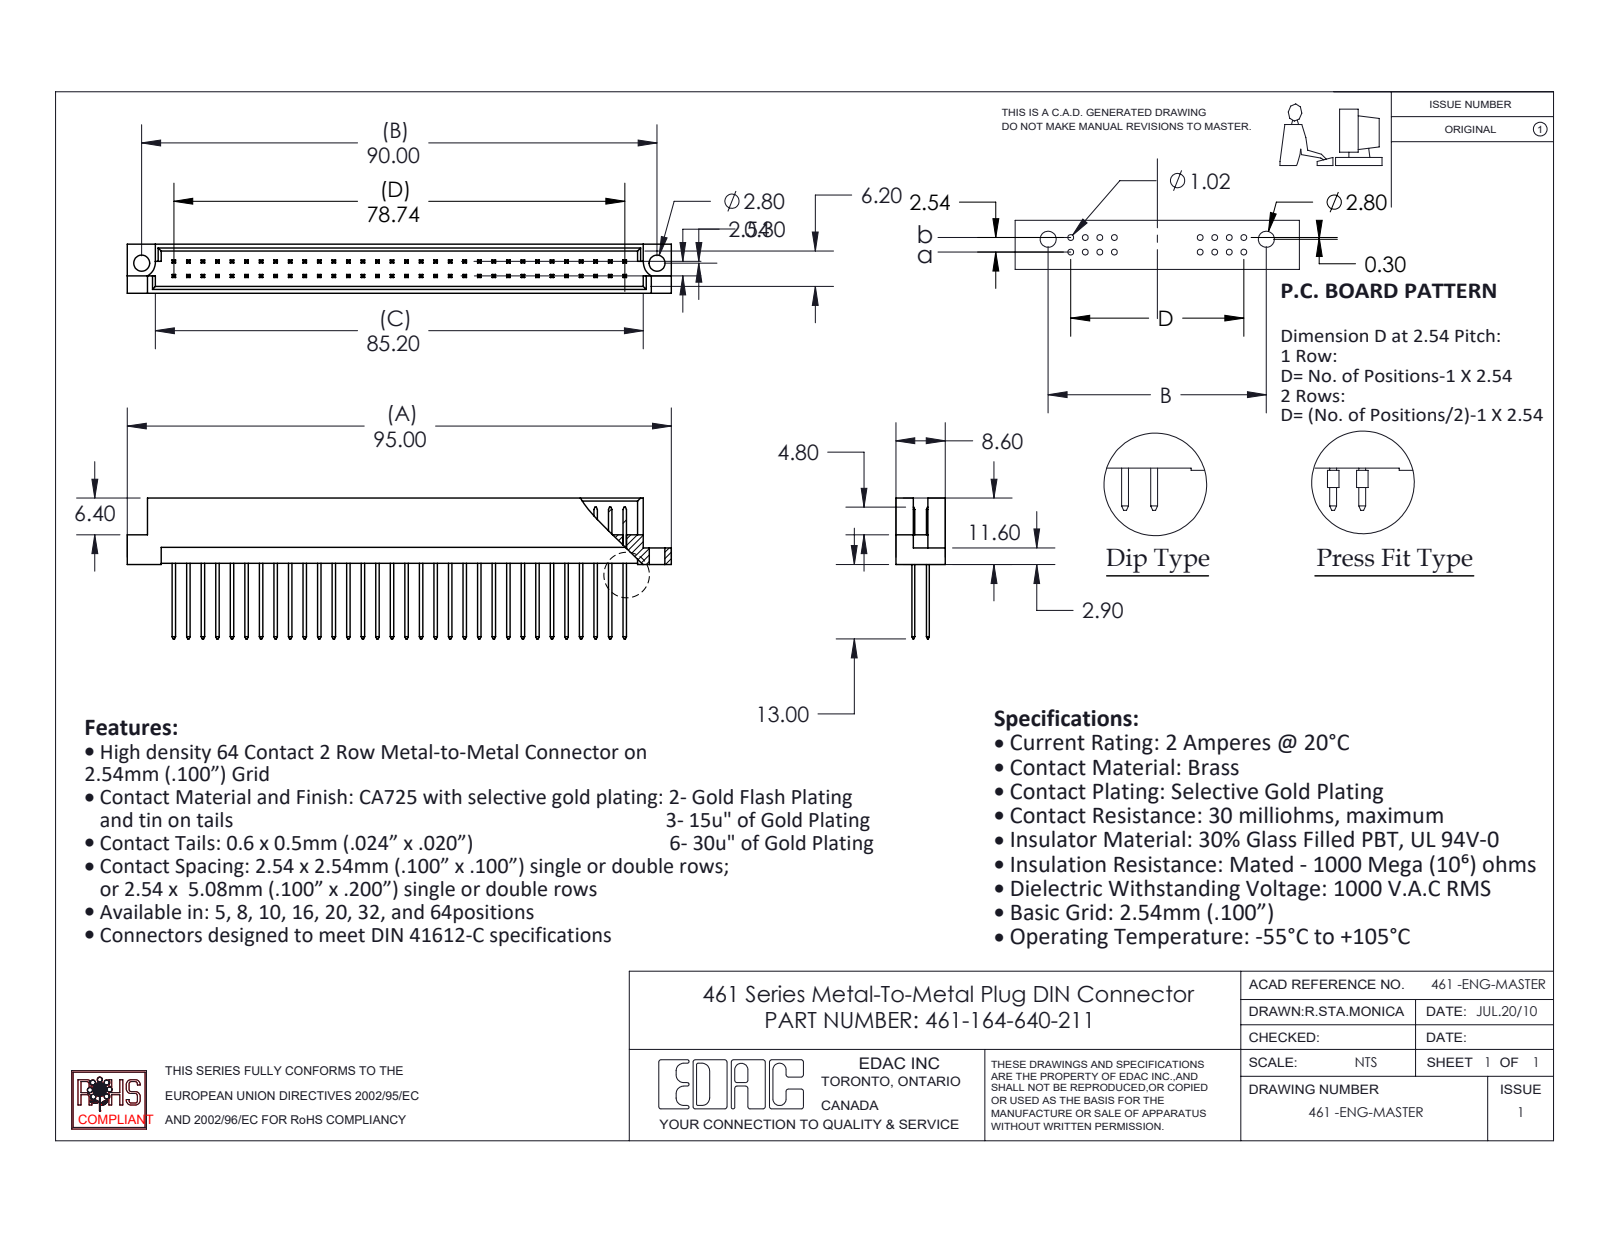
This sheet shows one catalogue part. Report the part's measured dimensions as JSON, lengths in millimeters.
{"part_name": "461 Part_64; 461-290_40; 461-164-640-211", "step_written_by": "SolidWorks 2020 (CONFIG_CONTROL_DESIGN)", "units": "millimeters", "bodies": {"solids": 65, "faces": 1201, "planar": 1194, "cylindrical": 7, "other": 0}, "overall_size": [95, 24.6, 8.6], "volume_mm3": 5091, "surface_area_mm2": 8885, "round_holes": [[2.8, 2]], "partial_cylinders_radius": [[2.8, 2]], "face_to_face_distances": [2.54, 1.2, 7.4, 2.78, 3.28, 5.32, 5.82, 1.58, 2.08, 4.12], "hole_center_spacings": [90]}
